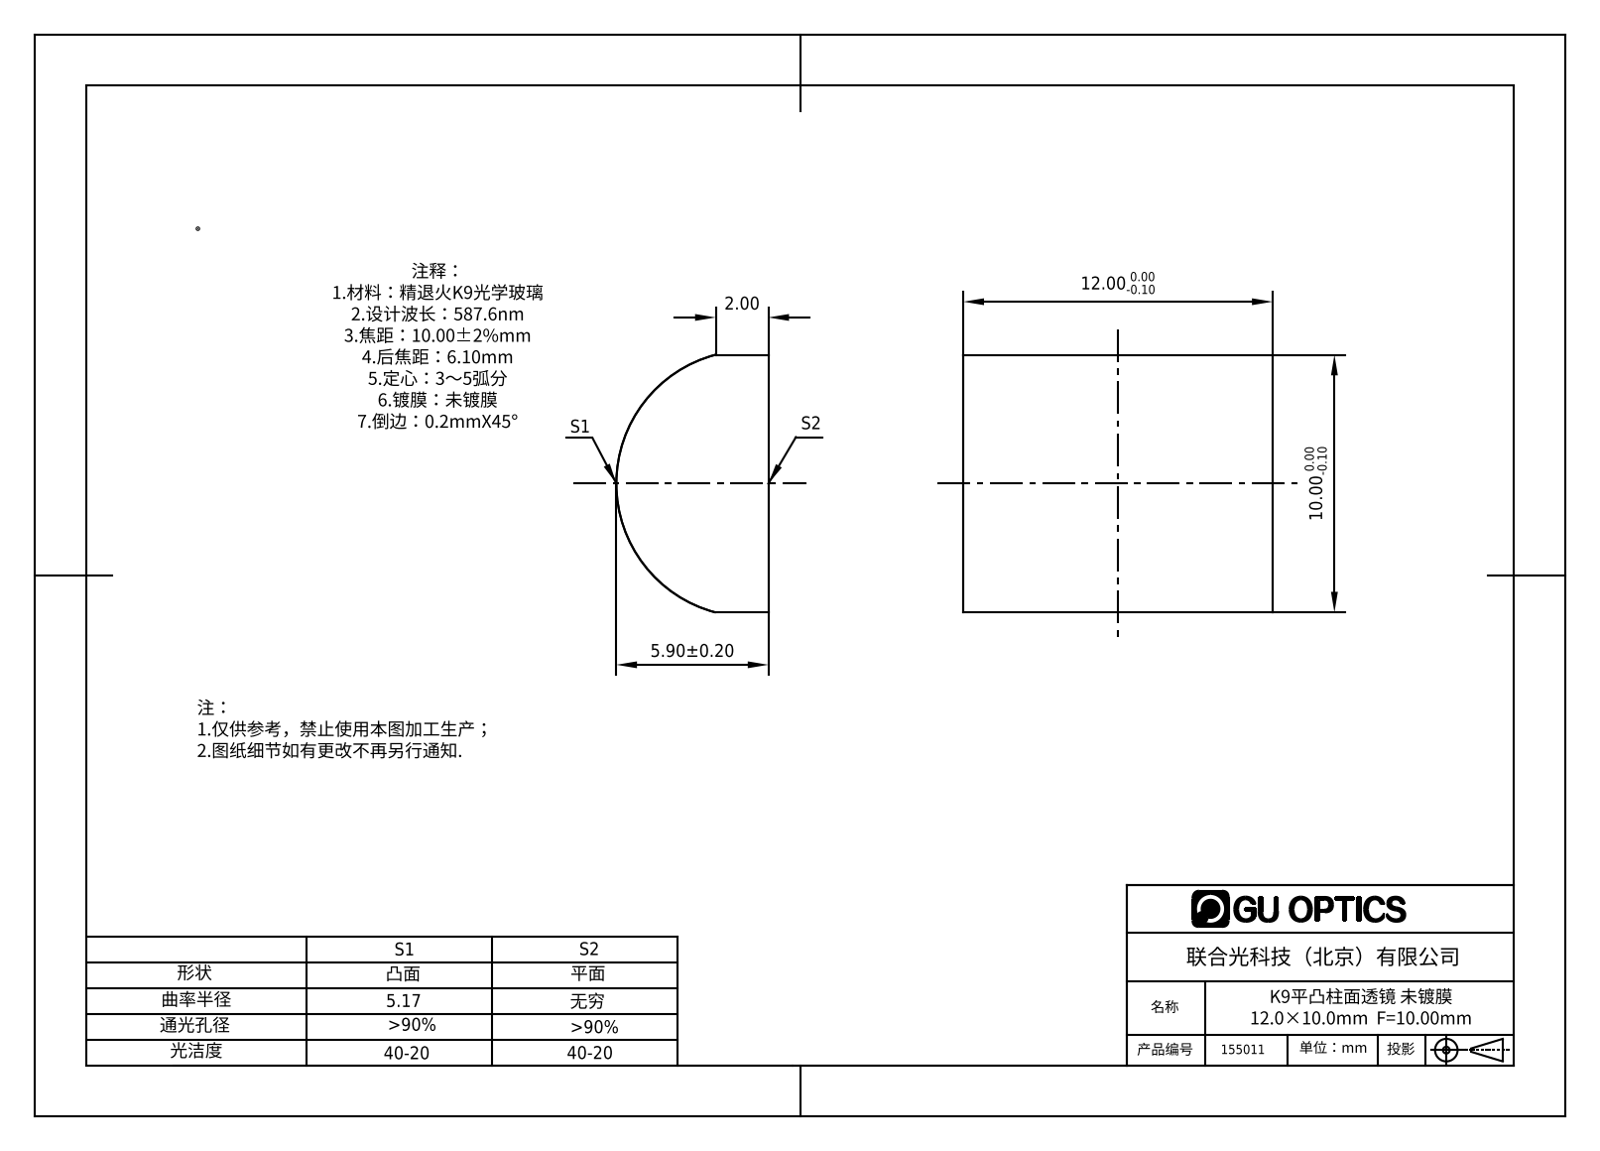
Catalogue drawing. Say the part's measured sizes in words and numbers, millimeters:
The part is named "155011". Its 3-D file was written by "SolidWorks 2016 (AUTOMOTIVE_DESIGN)". It is 1 solid with 6 faces: 5 planar, 1 cylindrical and 0 other. Overall it measures 12 by 10 by 5.9 millimeters. Its volume is 588 cubic millimeters and its surface area 430 square millimeters. Partial cylindrical surfaces (rounded edges, fillets, slot ends): 1 of radius 5.17. The main face-to-face distances are 12, 10.
